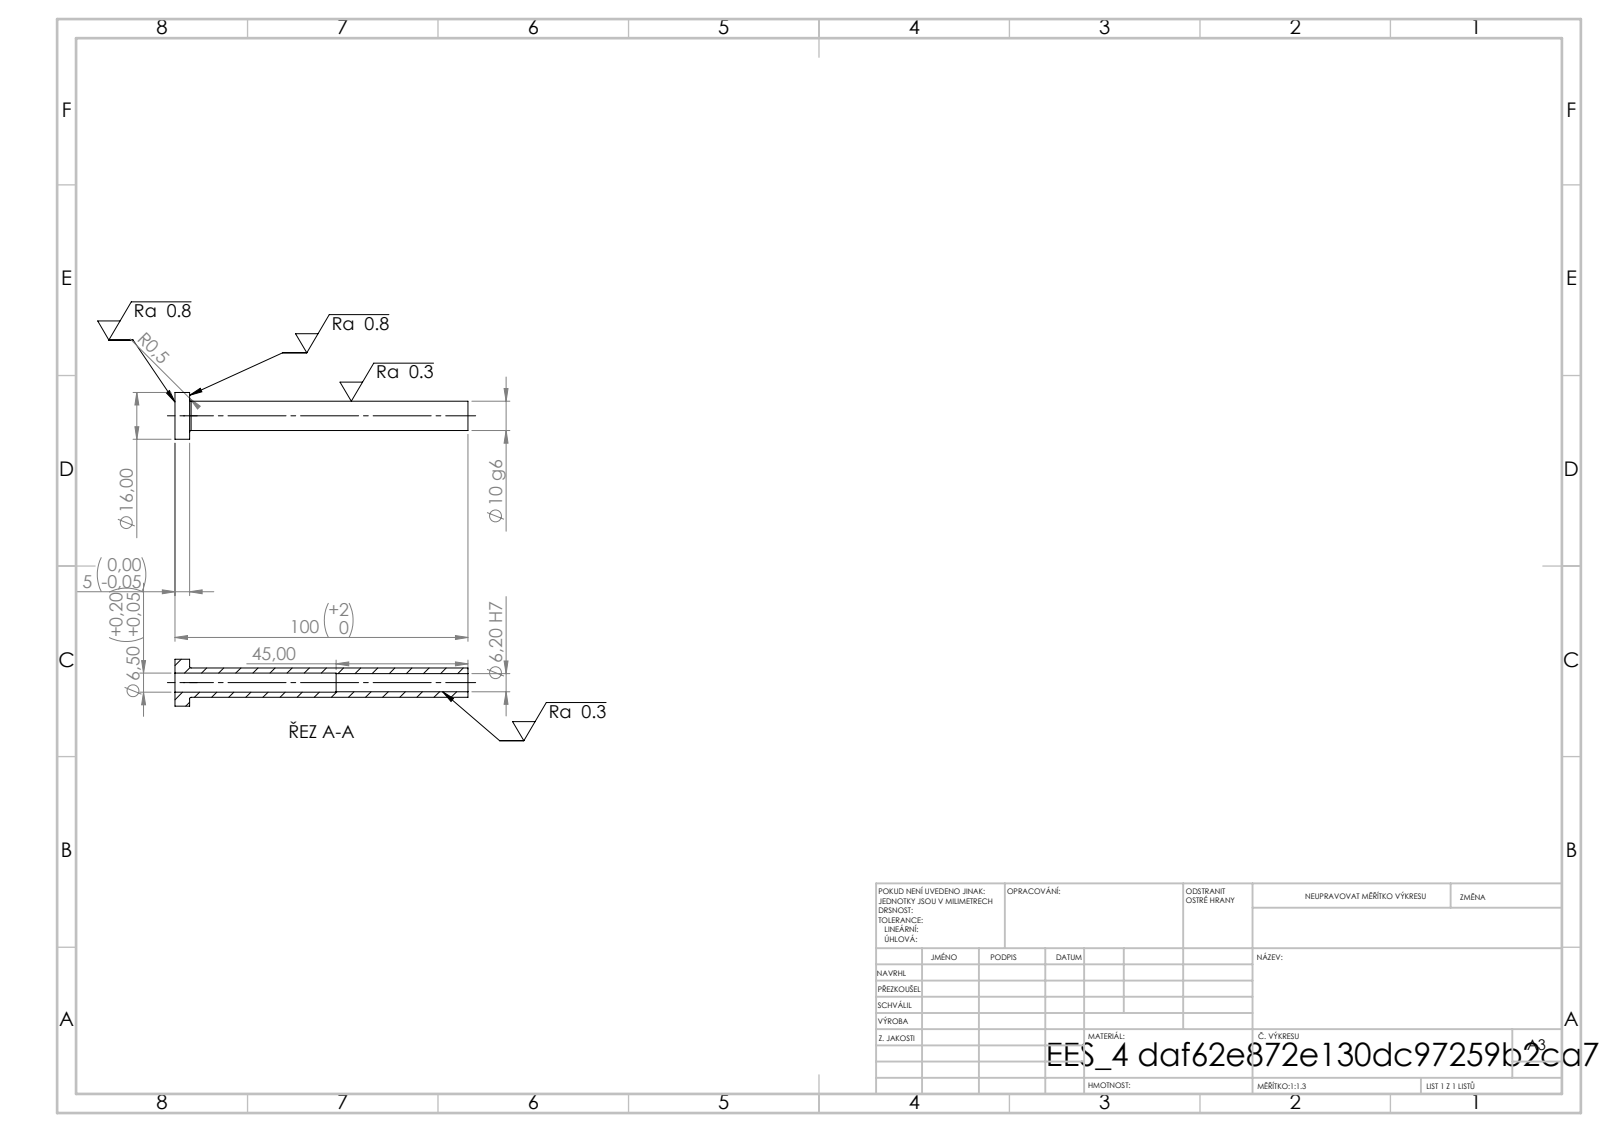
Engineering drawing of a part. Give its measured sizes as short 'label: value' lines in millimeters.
written by: SolidWorks 2019 (CONFIG_CONTROL_DESIGN)
unit: mm
bodies: 1 solid, 14 faces (4 planar, 8 cylindrical, 2 other)
size: 100 × 16 × 16
volume: 5 285 mm³; area: 5 571 mm²
holes: 1× ⌀6.2, 1× ⌀6.5
bosses: 1× ⌀16, 1× ⌀10
face distances: 5, 100, 95, 55, 50, 45
